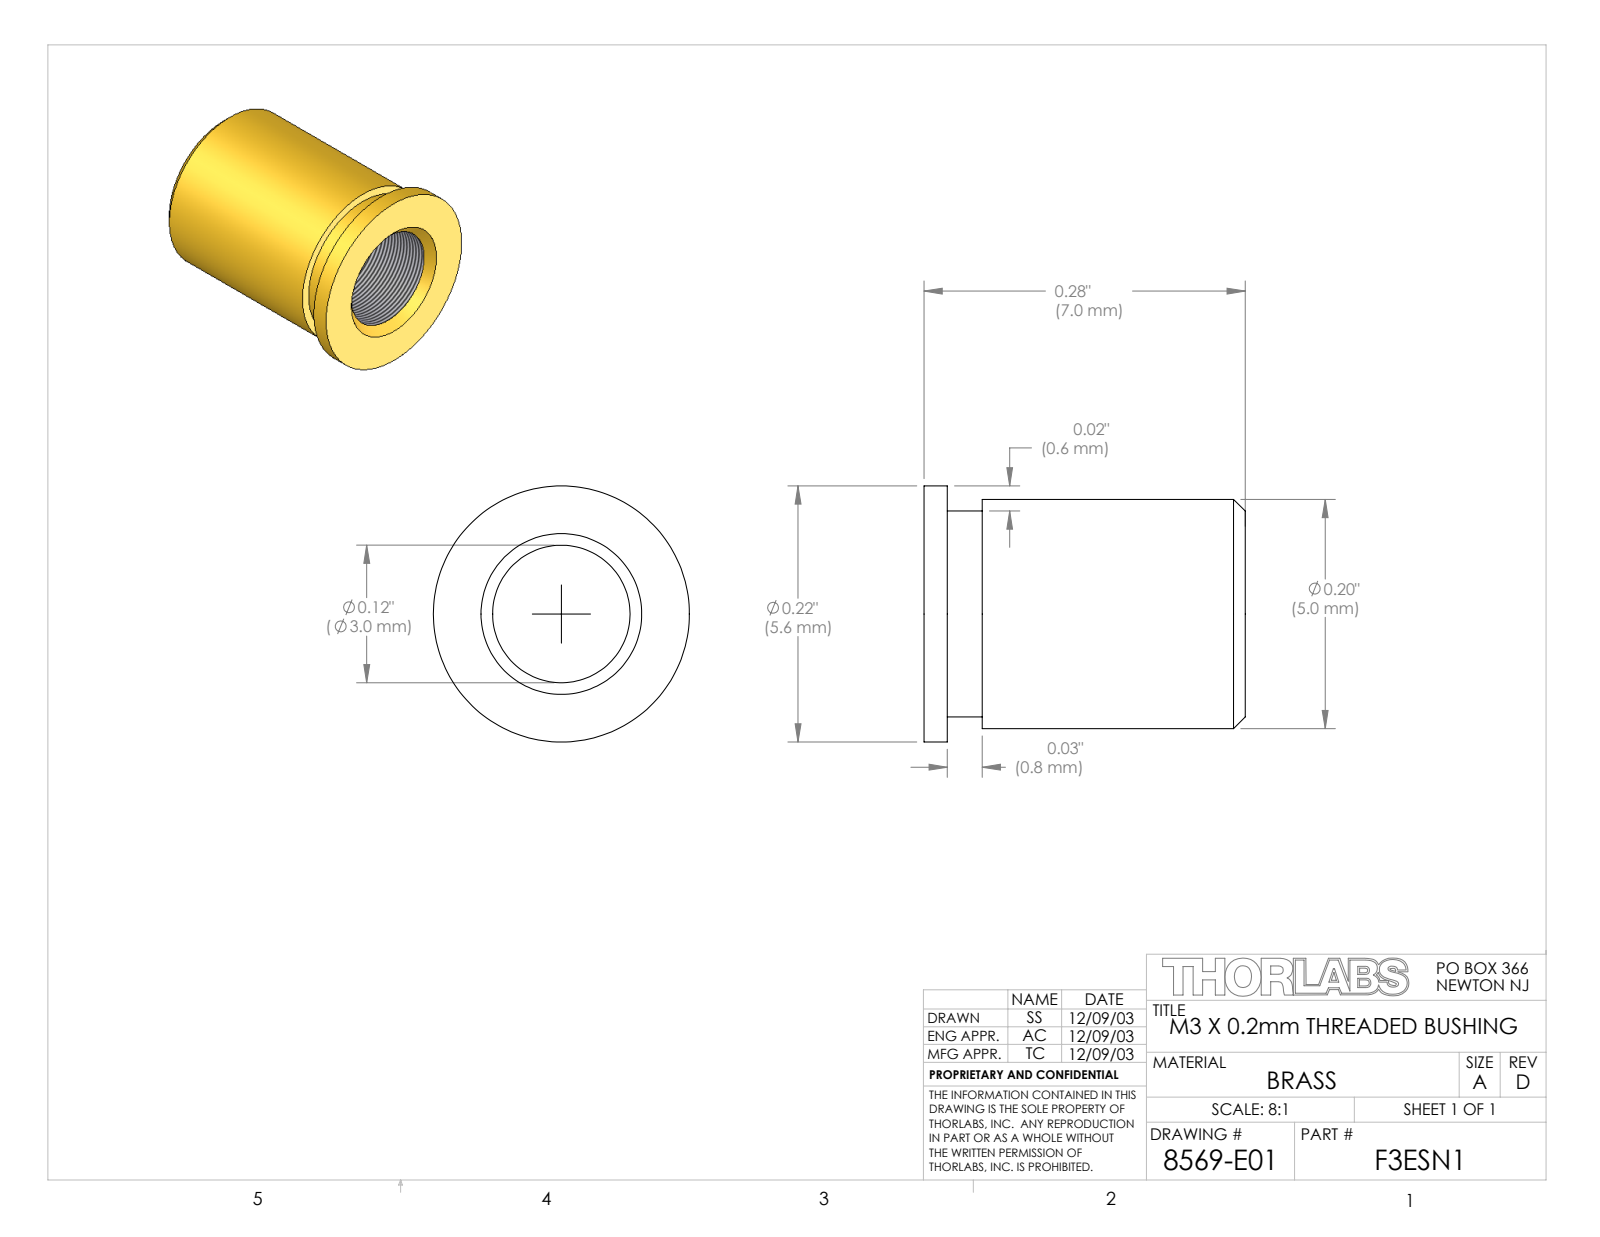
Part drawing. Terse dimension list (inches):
name: 8569-E0W
written by: SolidWorks 2007 (AUTOMOTIVE_DESIGN)
unit: in
bodies: 1 solid, 11 faces (3 planar, 4 cylindrical, 4 other)
size: 0.28 × 0.22 × 0.22
volume: 0.006 in³; area: 0.421 in²
bosses: 1× ⌀0.22, 1× ⌀0.197
face distances: 0.28, 0.02, 0.26
